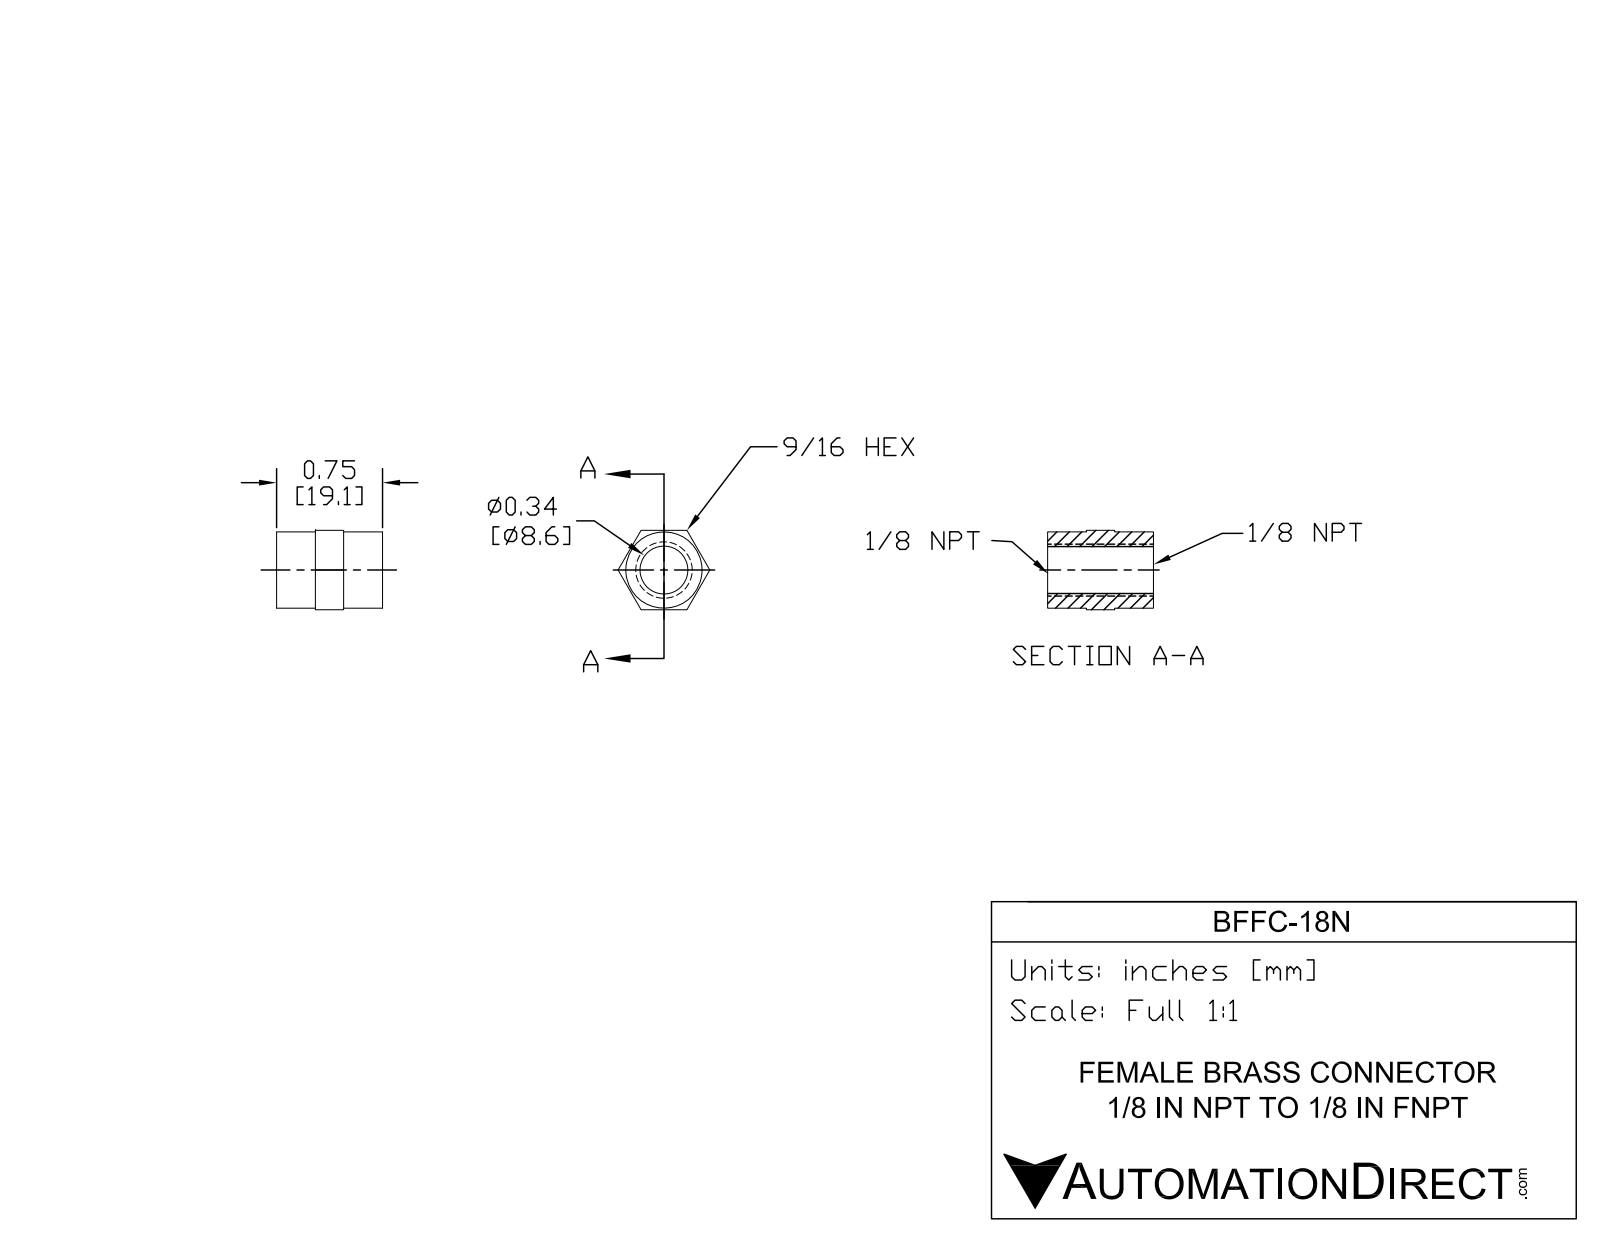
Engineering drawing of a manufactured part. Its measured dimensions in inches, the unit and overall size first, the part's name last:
Units: inches
Overall size (bounding box): 0.75 × 0.65 × 0.562
Round holes (diameter × count): ⌀0.34 ×1
Round bosses / shafts (diameter × count): ⌀0.525 ×1
Main face-to-face distances: 0.562, 0.75, 0.275, 0.475, 0.2
Volume: 0.106 in³ · Surface area: 2.464 in²
Bodies: 1 solid, 16 faces (10 planar, 6 cylindrical, 0 other)
Part name (STEP PRODUCT): BFFC-18N
STEP written by: SolidWorks 2015 (CONFIG_CONTROL_DESIGN)
